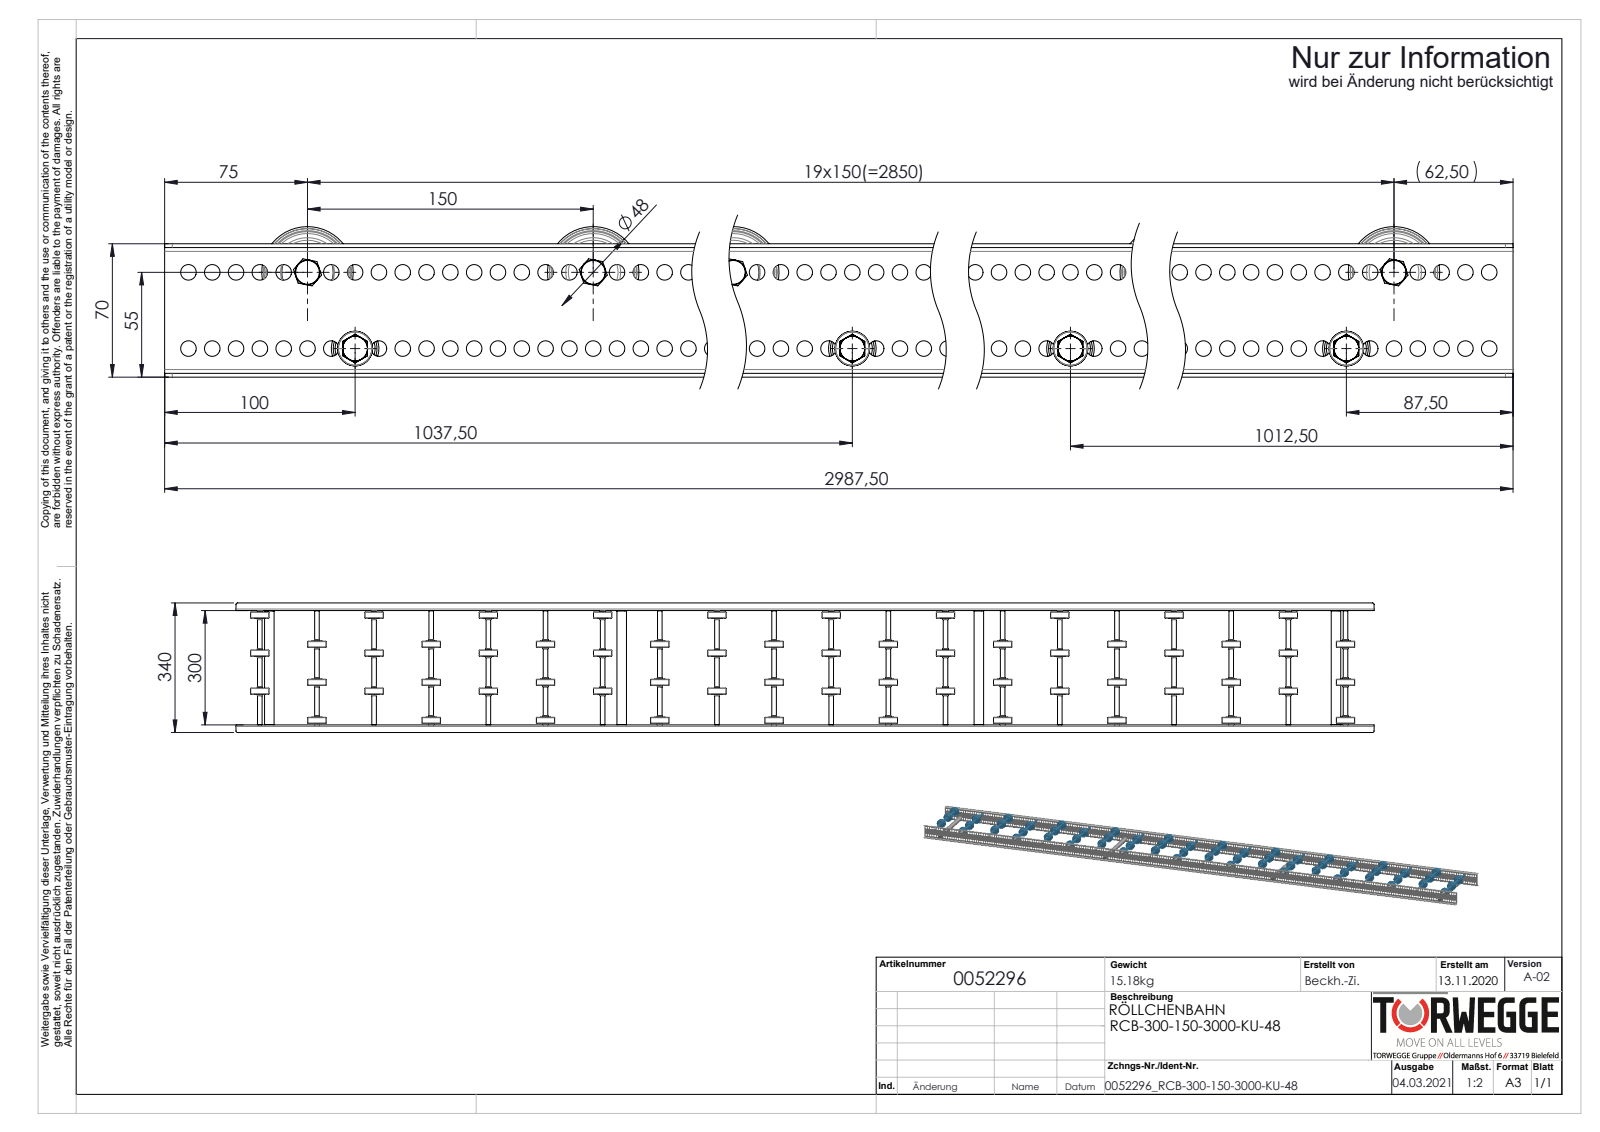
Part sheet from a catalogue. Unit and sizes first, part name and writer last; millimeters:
Units: millimetres
Overall size (bounding box): 2987.5 × 340 × 79
Round holes (diameter × count): ⌀8.2 ×476, ⌀6.65 ×20, ⌀9.65 ×20, ⌀13.7 ×20, ⌀6.8 ×4, ⌀21 ×4
Round bosses / shafts (diameter × count): ⌀8 ×24, ⌀48 ×20, ⌀27 ×20, ⌀12.7 ×20, ⌀12.5 ×20, ⌀12 ×20, ⌀25 ×4
Partial cylindrical surfaces — rounded edges, fillets, slot ends (radius × count): R4 ×8, R2 ×4
Main face-to-face distances: 2, 302, 68, 300, 304, 70, 66, 99.8, 16.3, 76.1
Hole centre spacings: 12.5, 25, 37.5, 50, 62.5, 75, 87.5, 100
Volume: 3 053 000 mm³ · Surface area: 2 496 000 mm²
Bodies: 202 solids, 8192 faces (1344 planar, 3520 cylindrical, 3328 other)
Part name (STEP PRODUCT): 0046278_KB-ROHR-12X1,75mm_KFG_L76; Traversen_KFG_L300; 0052296; S106837_Gewindestange-M8-KFG_L320 (+5 more)
STEP written by: SolidWorks 2020 (AUTOMOTIVE_DESIGN)
